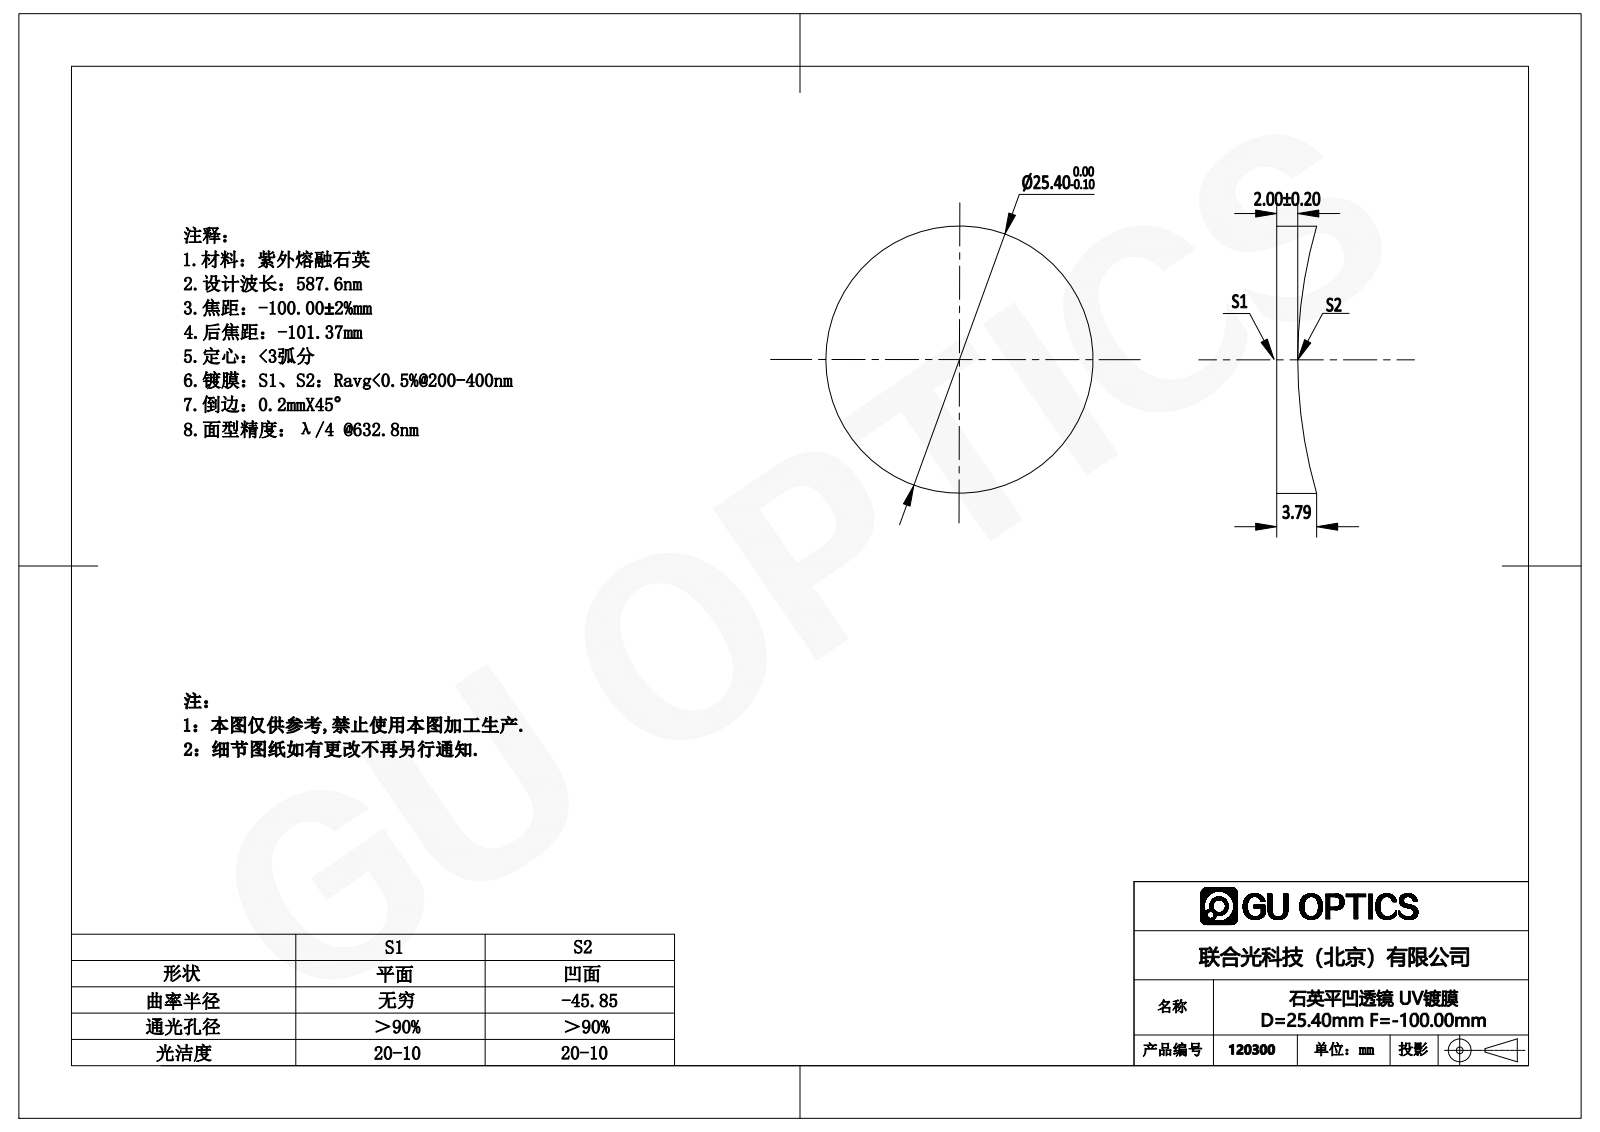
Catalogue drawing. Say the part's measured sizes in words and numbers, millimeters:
The part is named "120267". Its 3-D file was written by "SolidWorks 2016 (AUTOMOTIVE_DESIGN)". It is 1 solid with 5 faces: 1 planar, 2 cylindrical and 2 other. Overall it measures 25.4 by 25.4 by 3.79 millimeters. Its volume is 1 465 cubic millimeters and its surface area 1 326 square millimeters. Round bosses or shafts: 1 of diameter 25.4.
